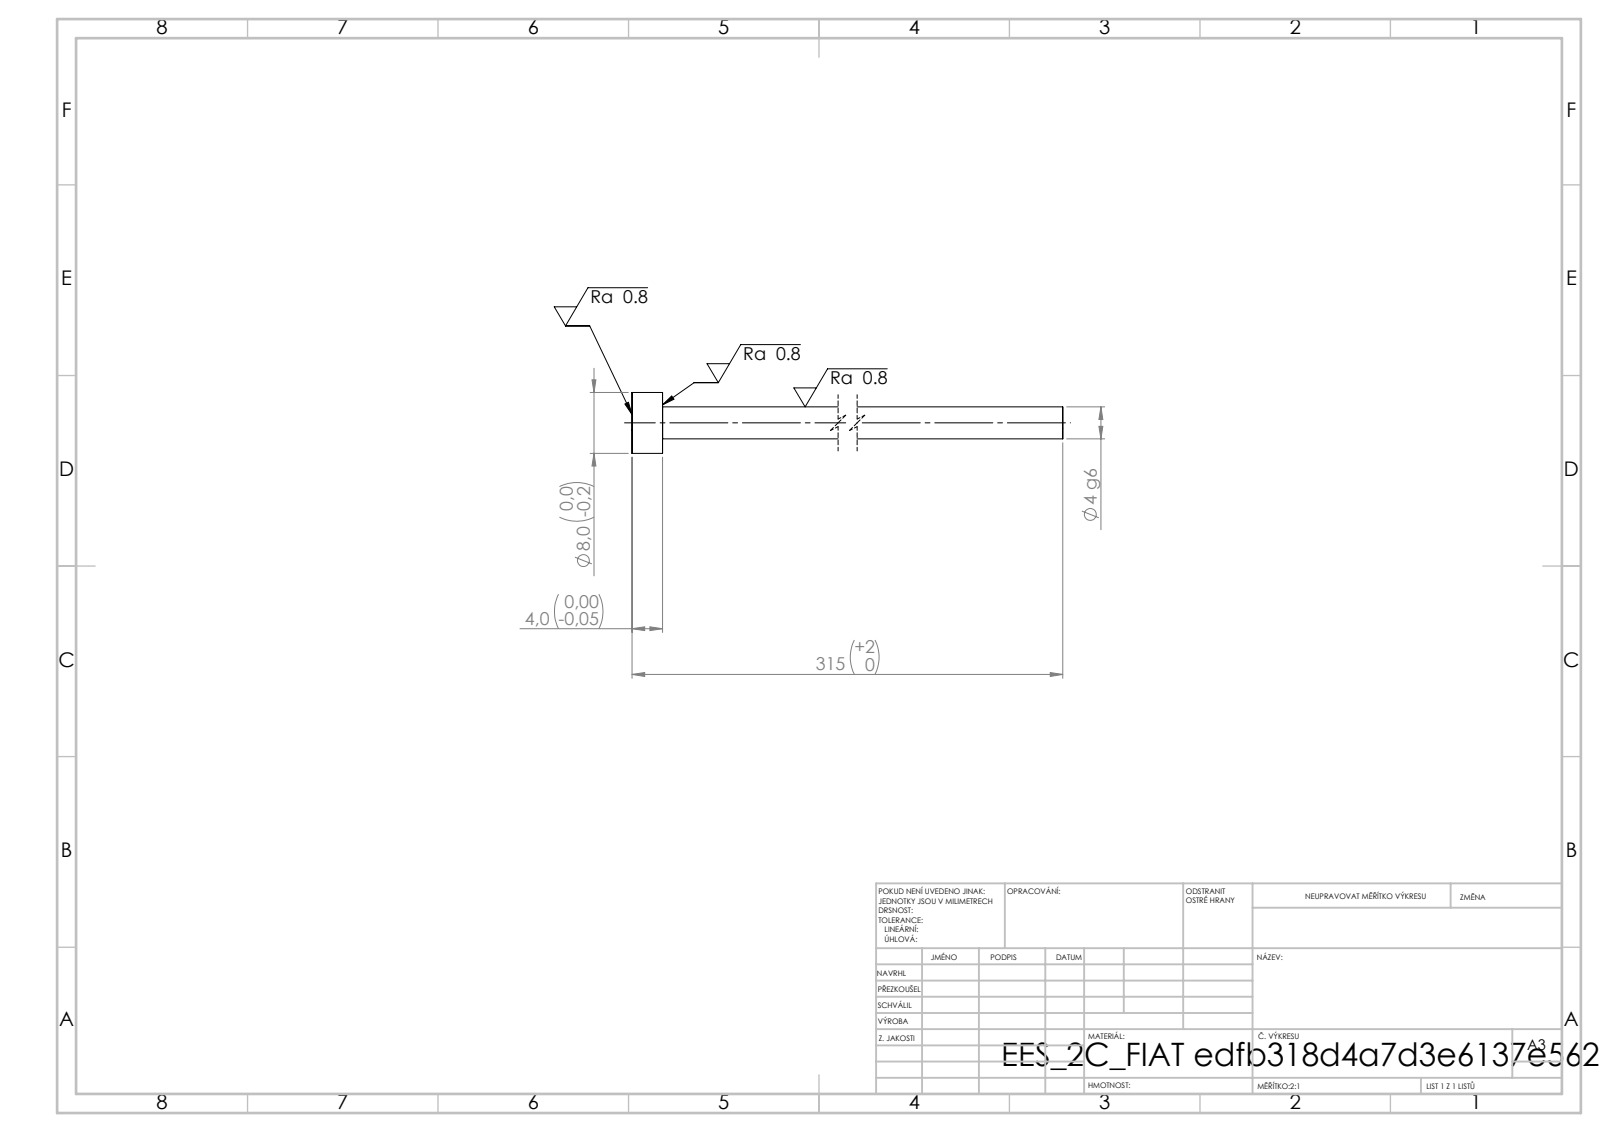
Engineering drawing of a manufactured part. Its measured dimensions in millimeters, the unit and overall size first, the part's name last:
Units: millimetres
Overall size (bounding box): 315 × 8 × 8
Round bosses / shafts (diameter × count): ⌀8 ×1, ⌀4.2 ×1
Main face-to-face distances: 4, 315, 311
Volume: 4 510 mm³ · Surface area: 4 305 mm²
Bodies: 1 solid, 7 faces (3 planar, 4 cylindrical, 0 other)
STEP written by: SolidWorks 2019 (CONFIG_CONTROL_DESIGN)
